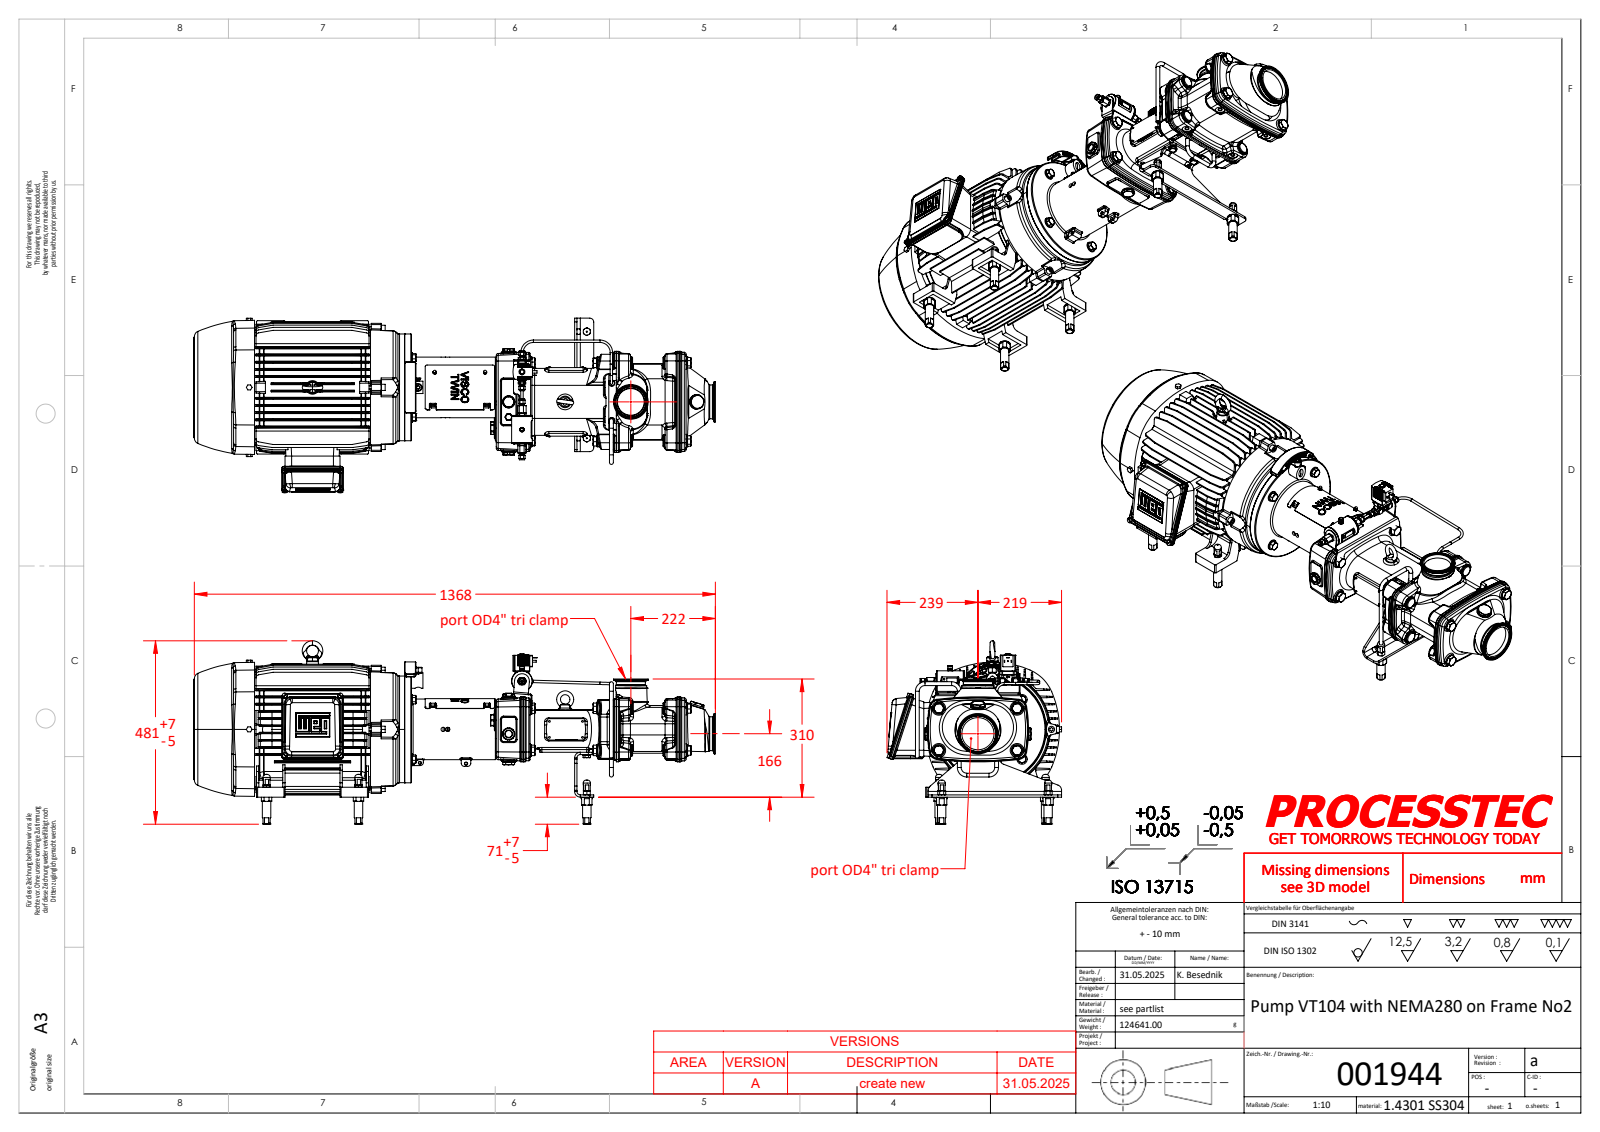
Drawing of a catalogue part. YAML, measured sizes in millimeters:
part_name: "001265; 001482; 001266; 001096 (+8 more)"
step_written_by: "SolidWorks 2023 (AUTOMOTIVE_DESIGN)"
units: millimeters
bodies: {solids: 119, faces: 9591, planar: 3349, cylindrical: 2215, other: 4027}
overall_size: [1369.64, 481.3, 458.2]
volume: 64730000
surface_area: 3878000
round_holes:
  - {diameter: 8, count: 13}
  - {diameter: 10.2, count: 10}
  - {diameter: 8.5, count: 9}
  - {diameter: 6.8, count: 8}
  - {diameter: 10.5, count: 8}
  - {diameter: 6, count: 7}
  - {diameter: 5.9, count: 6}
  - {diameter: 7.2, count: 6}
  - {diameter: 8.2, count: 6}
  - {diameter: 12, count: 6}
  - {diameter: 13.2, count: 6}
  - {diameter: 14.5, count: 6}
round_bosses_or_shafts:
  - {diameter: 8, count: 12}
  - {diameter: 6, count: 12}
  - {diameter: 30, count: 10}
  - {diameter: 10, count: 10}
  - {diameter: 24, count: 8}
  - {diameter: 5, count: 8}
  - {diameter: 22, count: 7}
  - {diameter: 19, count: 6}
partial_cylinders:
  - {radius: 2, count: 141}
  - {radius: 4, count: 85}
  - {radius: 5, count: 62}
  - {radius: 0.5, count: 60}
  - {radius: 3, count: 56}
  - {radius: 8, count: 54}
  - {radius: 1.5, count: 39}
  - {radius: 6, count: 26}
face_to_face_distances: [409.64, 305, 714.64, 18.67, 33.01, 14.34, 113.54, 146.55, 5.24, 189.19]
hole_center_spacings: [51, 55, 158.81, 58.87, 109.73, 28.75, 62.52, 62.81]
